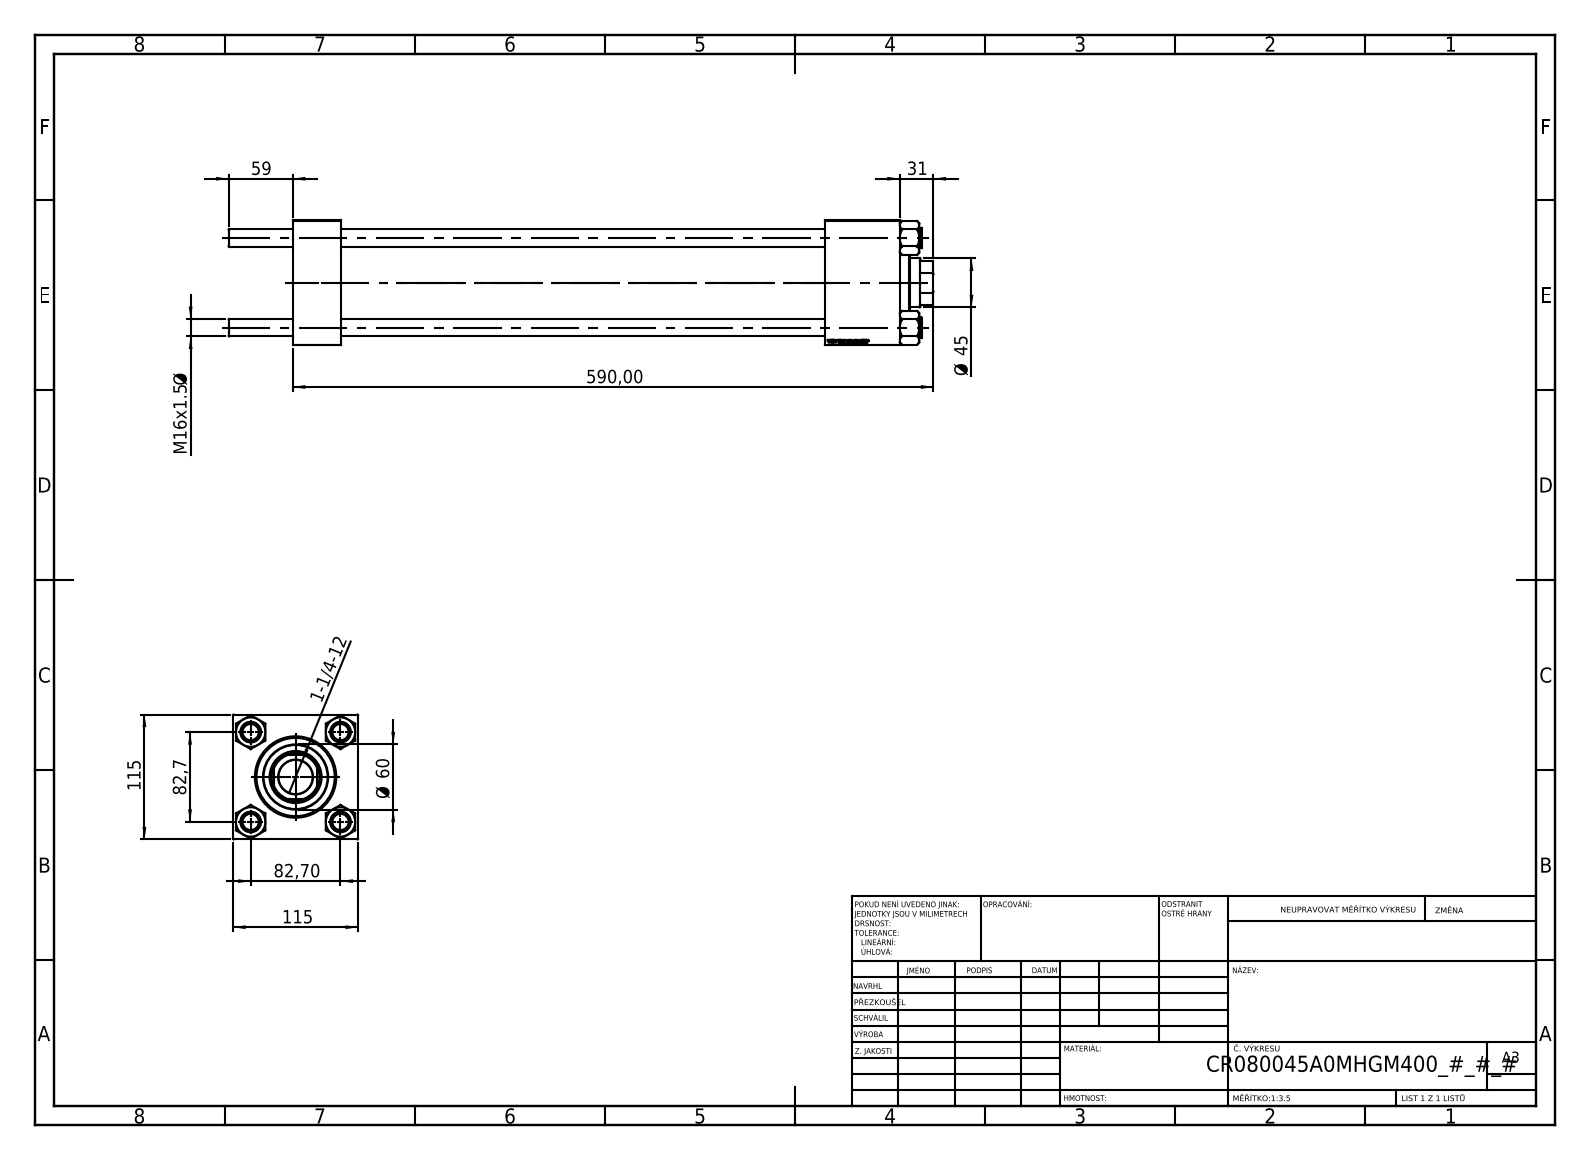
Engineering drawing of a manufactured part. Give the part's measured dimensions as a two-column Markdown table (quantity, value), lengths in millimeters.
| quantity | value |
| --- | --- |
| part name | V215_VC_A; V215CR_BODY_A; NUT_M5; V215CR_VCP (+1 more) |
| STEP written by | SolidWorks 2019 (CONFIG_CONTROL_DESIGN) |
| units | millimeters |
| bodies | 11 solids, 1182 faces (568 planar, 78 cylindrical, 536 other) |
| overall size | 649 × 115 × 115 |
| volume | 3 106 000 mm³ |
| surface area | 628 333 mm² |
| round holes (diameter × count) | 16 × 4, 7 × 2, 26.44 × 2, 35 × 2, 31.5 × 1, 45 × 1, 48 × 1, 61 × 1, 72 × 1, 80 × 1 |
| round bosses / shafts (diameter × count) | 19 × 4, 86 × 1, 60 × 1 |
| partial cylindrical surfaces (radius × count) | 22 × 1 |
| main face-to-face distances | 115, 44, 559, 515, 490, 446, 69, 530.3, 486.3, 40.3 |
| hole center spacings | 58.48, 82.7, 116.96, 491 |
